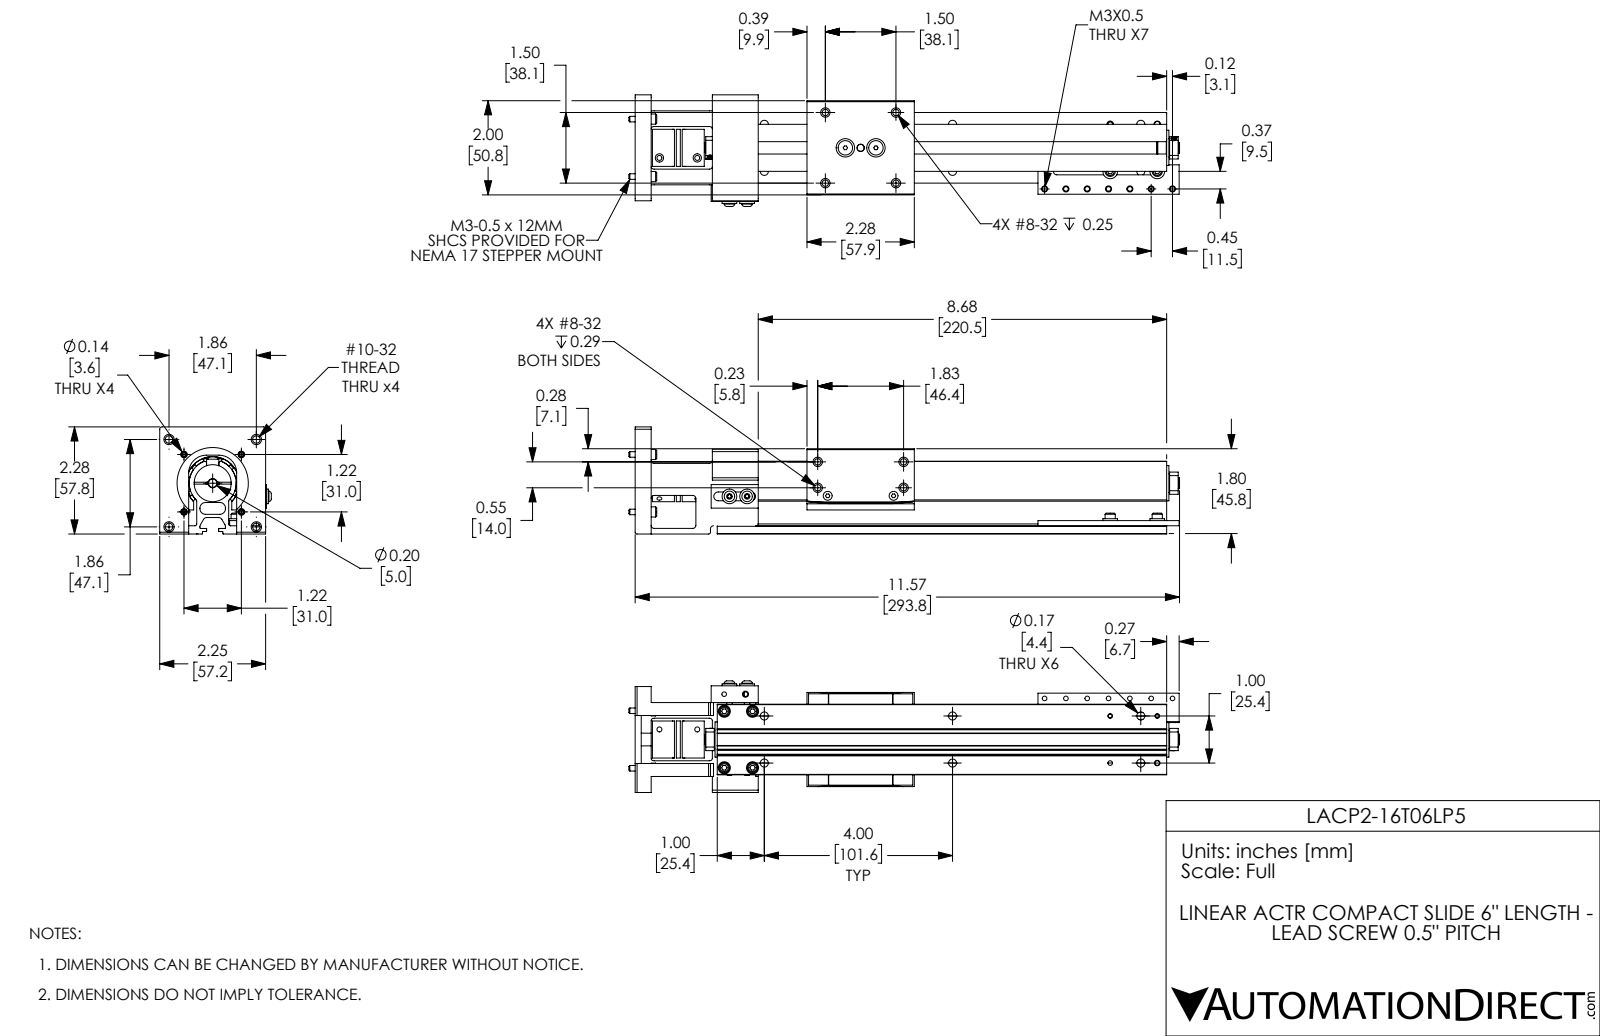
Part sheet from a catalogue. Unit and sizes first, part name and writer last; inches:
Units: inches
Overall size (bounding box): 11.7 × 2.37 × 2.275
Round holes (diameter × count): ⌀0.098 ×18, ⌀0.136 ×10, ⌀0.172 ×6, ⌀0.141 ×4, ⌀0.147 ×4, ⌀0.159 ×4, ⌀0.257 ×4, ⌀0.099 ×2, ⌀0.106 ×2, ⌀0.118 ×2, ⌀0.125 ×2, ⌀0.125 ×2
Round bosses / shafts (diameter × count): ⌀0.217 ×10, ⌀0.118 ×10, ⌀0.312 ×4, ⌀0.118 ×3, ⌀0.307 ×2, ⌀0.224 ×2, ⌀0.164 ×2, ⌀0.138 ×2
Partial cylindrical surfaces — rounded edges, fillets, slot ends (radius × count): R0.01 ×17, R0.05 ×9, R0.039 ×8, R0.065 ×7, R0.02 ×4, R0.074 ×4, R0.079 ×4, R0.118 ×4
Main face-to-face distances: 0.175, 0.34, 0.49, 0.17, 0.849, 0.446, 1.124, 0.661, 1.339, 1.51
Hole centre spacings: 1, 0.453, 0.863, 0.906, 1.312, 1.57, 1.856, 0.453
Volume: 14.82 in³ · Surface area: 224.2 in²
Bodies: 46 solids, 1236 faces (502 planar, 465 cylindrical, 269 other)
Part name (STEP PRODUCT): LACP2-16T06LP5; LACP2-16T06LP5_BLOCK; LACP2-16T06LP5_BODY
STEP written by: SolidWorks 2017 (AUTOMOTIVE_DESIGN)
